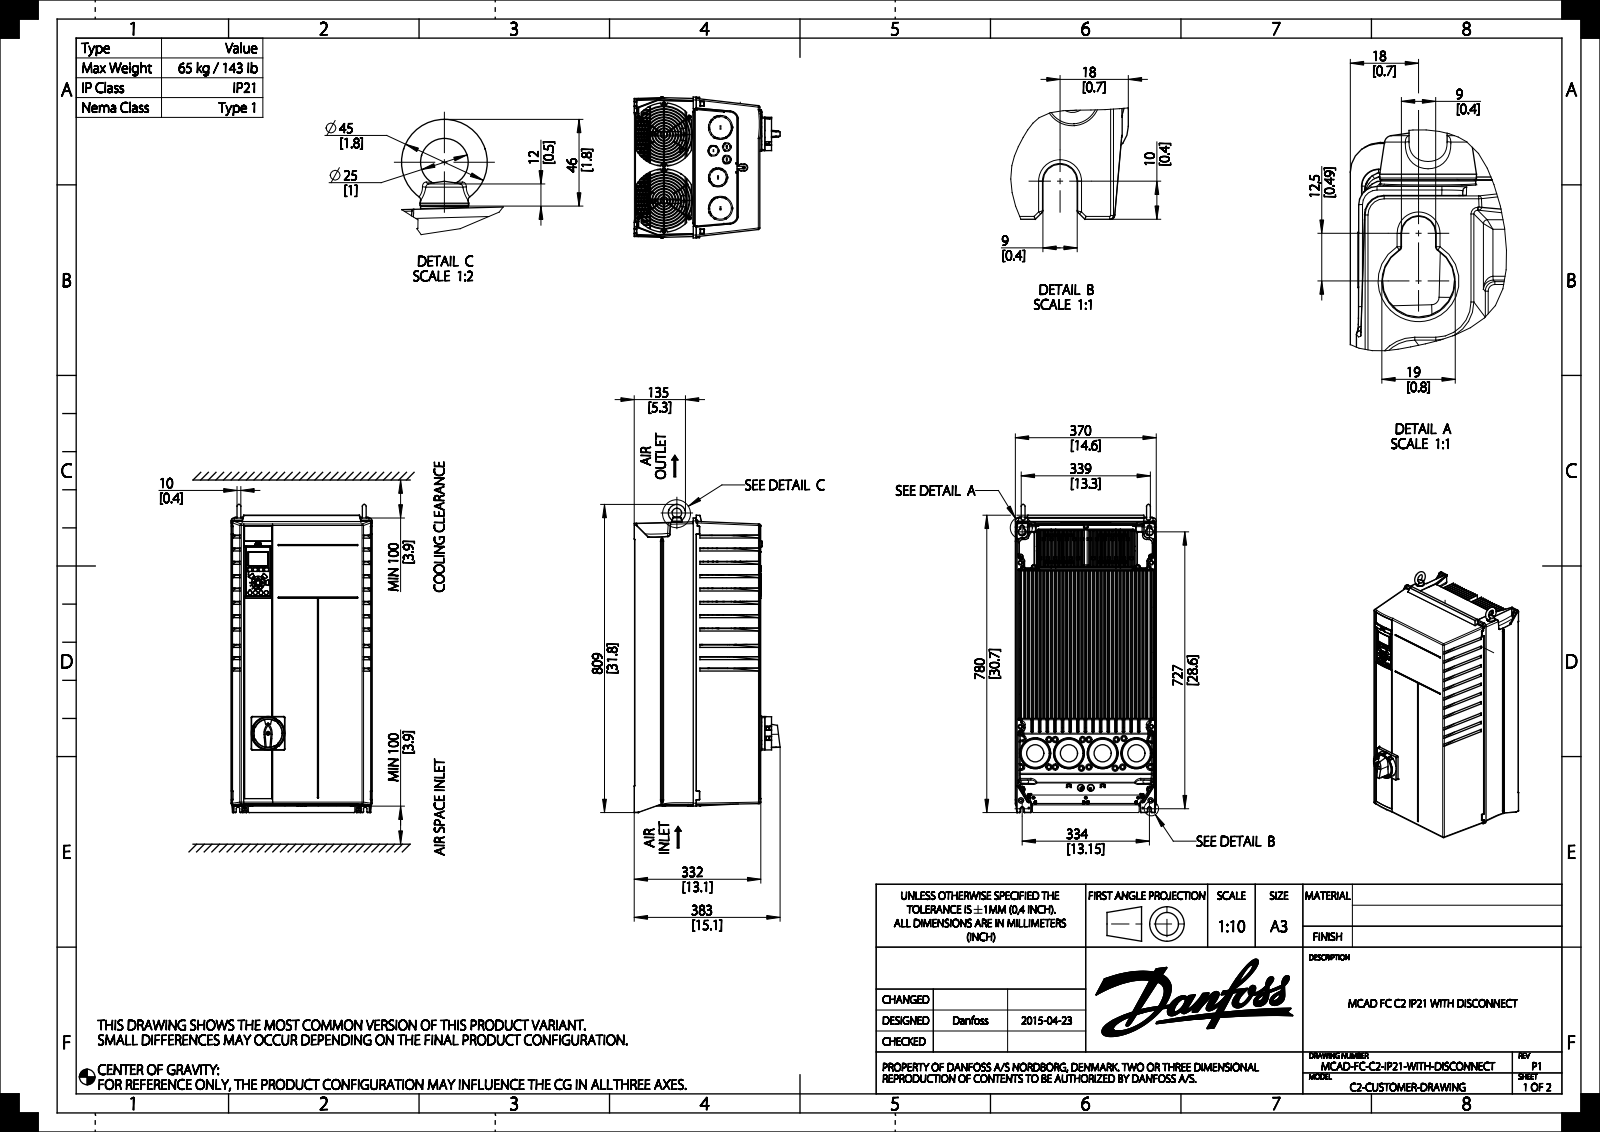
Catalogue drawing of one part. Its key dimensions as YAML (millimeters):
part_name: "DANFOSS-FC300-C2-IP21-SWITCH-18"
step_written_by: "CREO PARAMETRIC BY PTC INC, 2018070 (CONFIG_CONTROL_DESIGN)"
units: millimeters
bodies: {solids: 1, faces: 4778, planar: 1603, cylindrical: 1593, other: 1582}
overall_size: [780.17, 392.7, 369.82]
volume: 67920000
surface_area: 3485000
round_holes:
  - {diameter: 4.2, count: 27}
  - {diameter: 5.5, count: 10}
  - {diameter: 4, count: 4}
  - {diameter: 2, count: 3}
  - {diameter: 3.5, count: 3}
  - {diameter: 5.2, count: 2}
  - {diameter: 6, count: 2}
  - {diameter: 63.3, count: 2}
  - {diameter: 12, count: 1}
  - {diameter: 14, count: 1}
  - {diameter: 26.3, count: 1}
  - {diameter: 50.2, count: 1}
round_bosses_or_shafts:
  - {diameter: 5, count: 9}
  - {diameter: 2.3, count: 9}
  - {diameter: 8, count: 8}
  - {diameter: 3.58, count: 8}
  - {diameter: 7.5, count: 3}
  - {diameter: 25, count: 2}
  - {diameter: 14.5, count: 2}
  - {diameter: 57.1, count: 1}
partial_cylinders:
  - {radius: 1, count: 198}
  - {radius: 0.5, count: 197}
  - {radius: 2.5, count: 96}
  - {radius: 0.75, count: 73}
  - {radius: 3, count: 65}
  - {radius: 0.35, count: 64}
  - {radius: 0.2, count: 52}
  - {radius: 1.5, count: 36}
face_to_face_distances: [20, 40, 60, 80, 100, 120, 140, 160, 180, 200]
hole_center_spacings: [206.5, 352, 408.1, 332, 394.51, 17.89, 29.55, 37.61]
